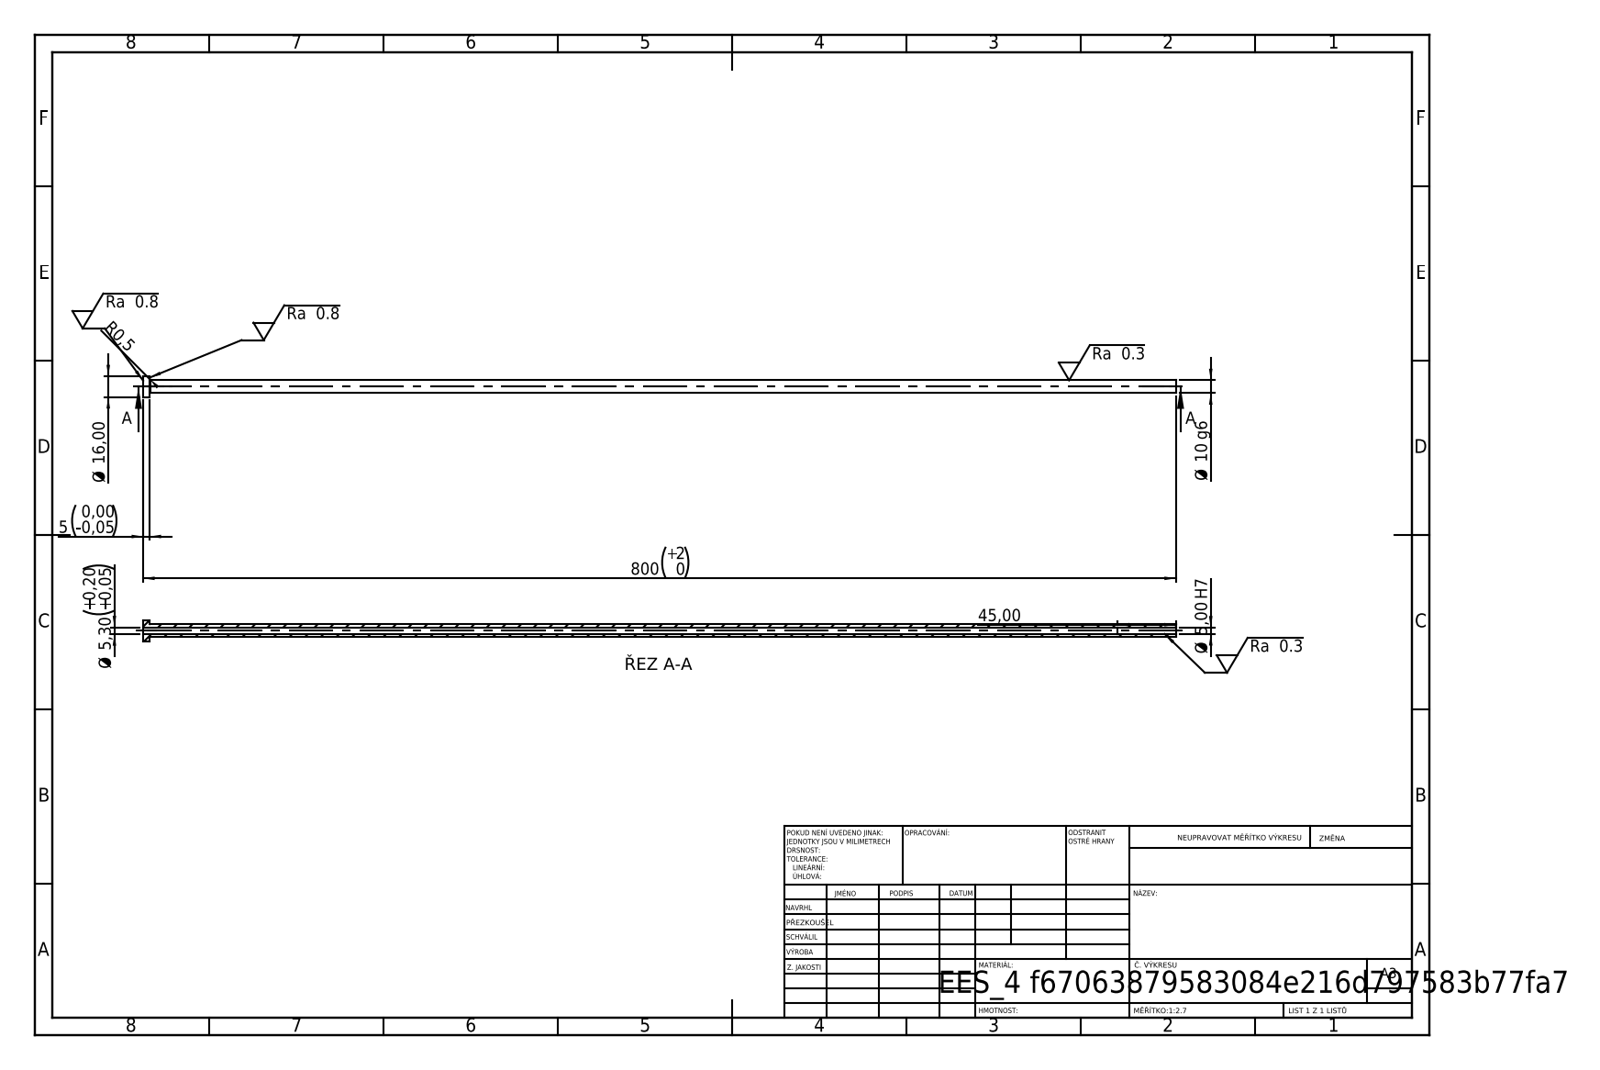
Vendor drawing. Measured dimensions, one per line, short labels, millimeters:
written by: SolidWorks 2019 (CONFIG_CONTROL_DESIGN)
unit: mm
bodies: 1 solid, 14 faces (4 planar, 8 cylindrical, 2 other)
size: 800 × 16 × 16
volume: 45 906 mm³; area: 38 861 mm²
holes: 1× ⌀5, 1× ⌀5.3
bosses: 1× ⌀16, 1× ⌀10
face distances: 5, 800, 795, 755, 750, 45
